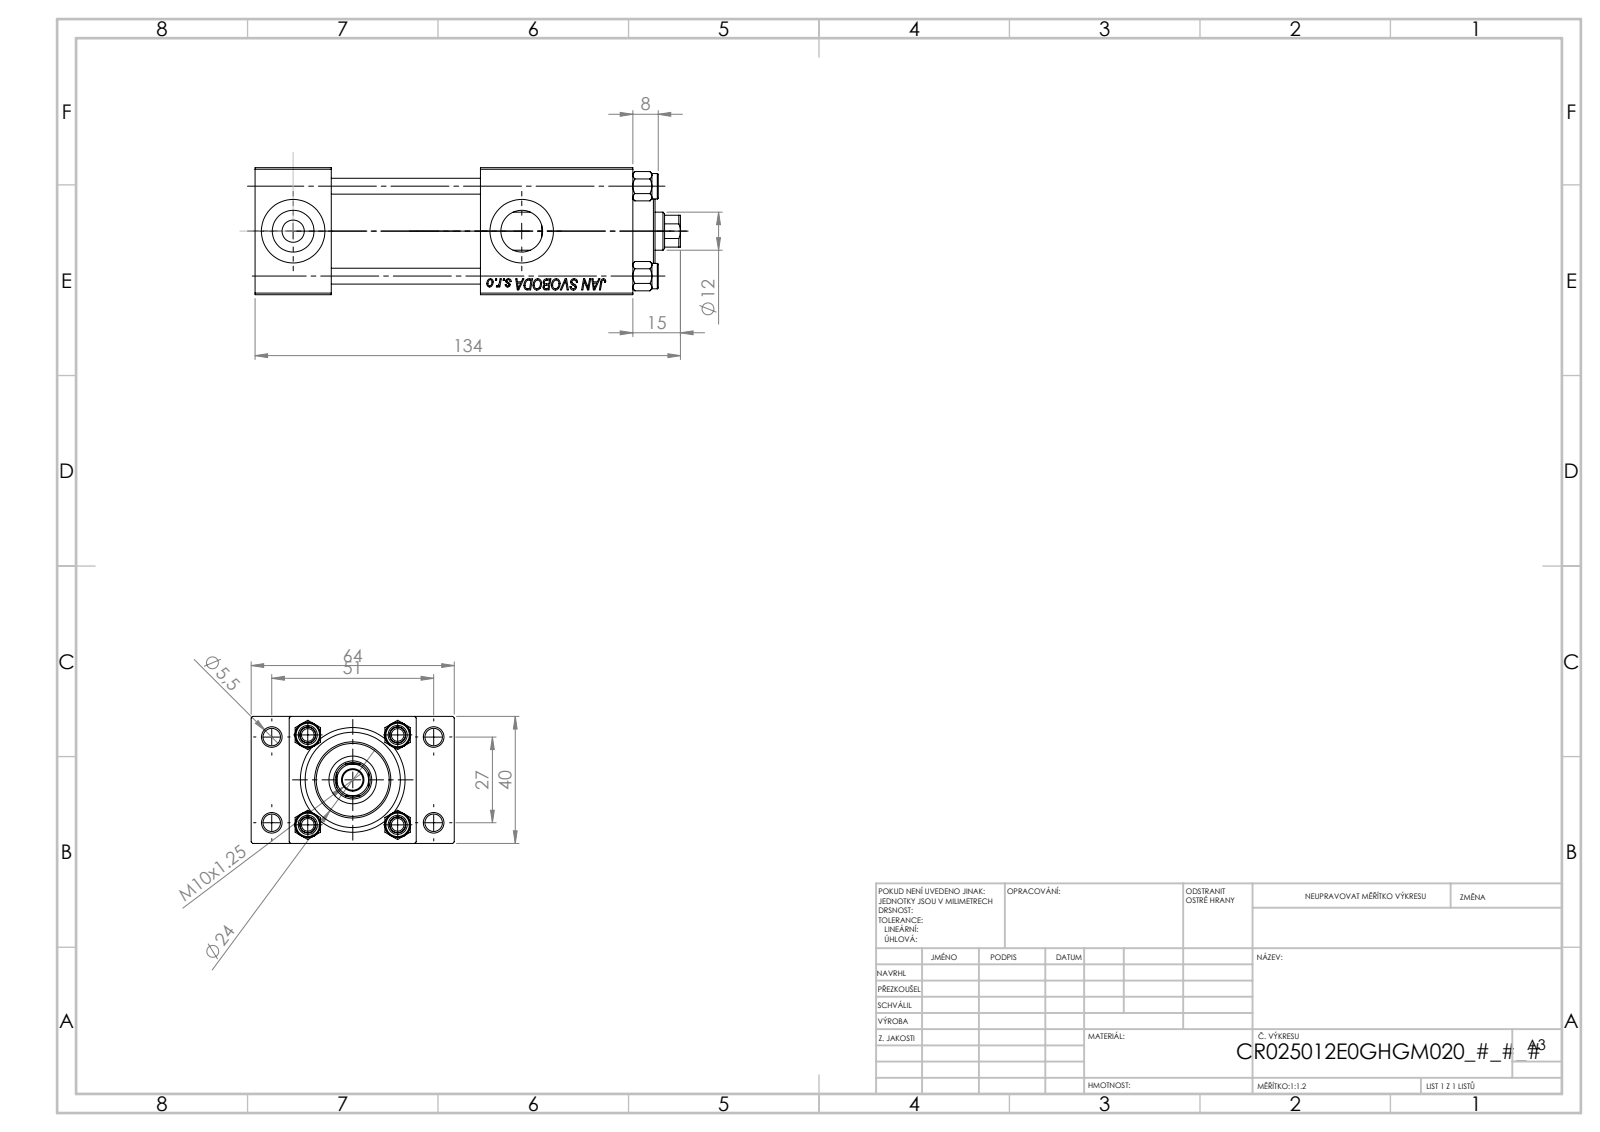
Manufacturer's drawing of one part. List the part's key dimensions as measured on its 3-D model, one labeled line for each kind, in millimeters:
Part name (STEP PRODUCT): V215_VC_A; V215CR_TYCINKA_E; V215CR_VCP_E; V215CR_E_Body (+1 more)
STEP written by: SolidWorks 2019 (CONFIG_CONTROL_DESIGN)
Units: millimetres
Bodies: 11 solids, 1135 faces (497 planar, 86 cylindrical, 552 other)
Overall size (bounding box): 134 × 64 × 40
Volume: 163 534 mm³ · Surface area: 62 368 mm²
Round holes (diameter × count): ⌀5 ×4, ⌀5.5 ×4, ⌀20 ×3, ⌀7 ×2, ⌀13.16 ×2, ⌀6.5 ×1, ⌀12 ×1, ⌀15 ×1, ⌀25 ×1, ⌀30 ×1
Round bosses / shafts (diameter × count): ⌀8 ×4, ⌀31 ×1, ⌀24 ×1
Partial cylindrical surfaces — rounded edges, fillets, slot ends (radius × count): R5.5 ×1
Main face-to-face distances: 40, 24, 12, 52, 119, 95, 90.3, 66.3, 28.7, 47
Hole centre spacings: 11.37, 20.01, 28.3, 28.85, 29.89, 39.66, 48.34, 27
